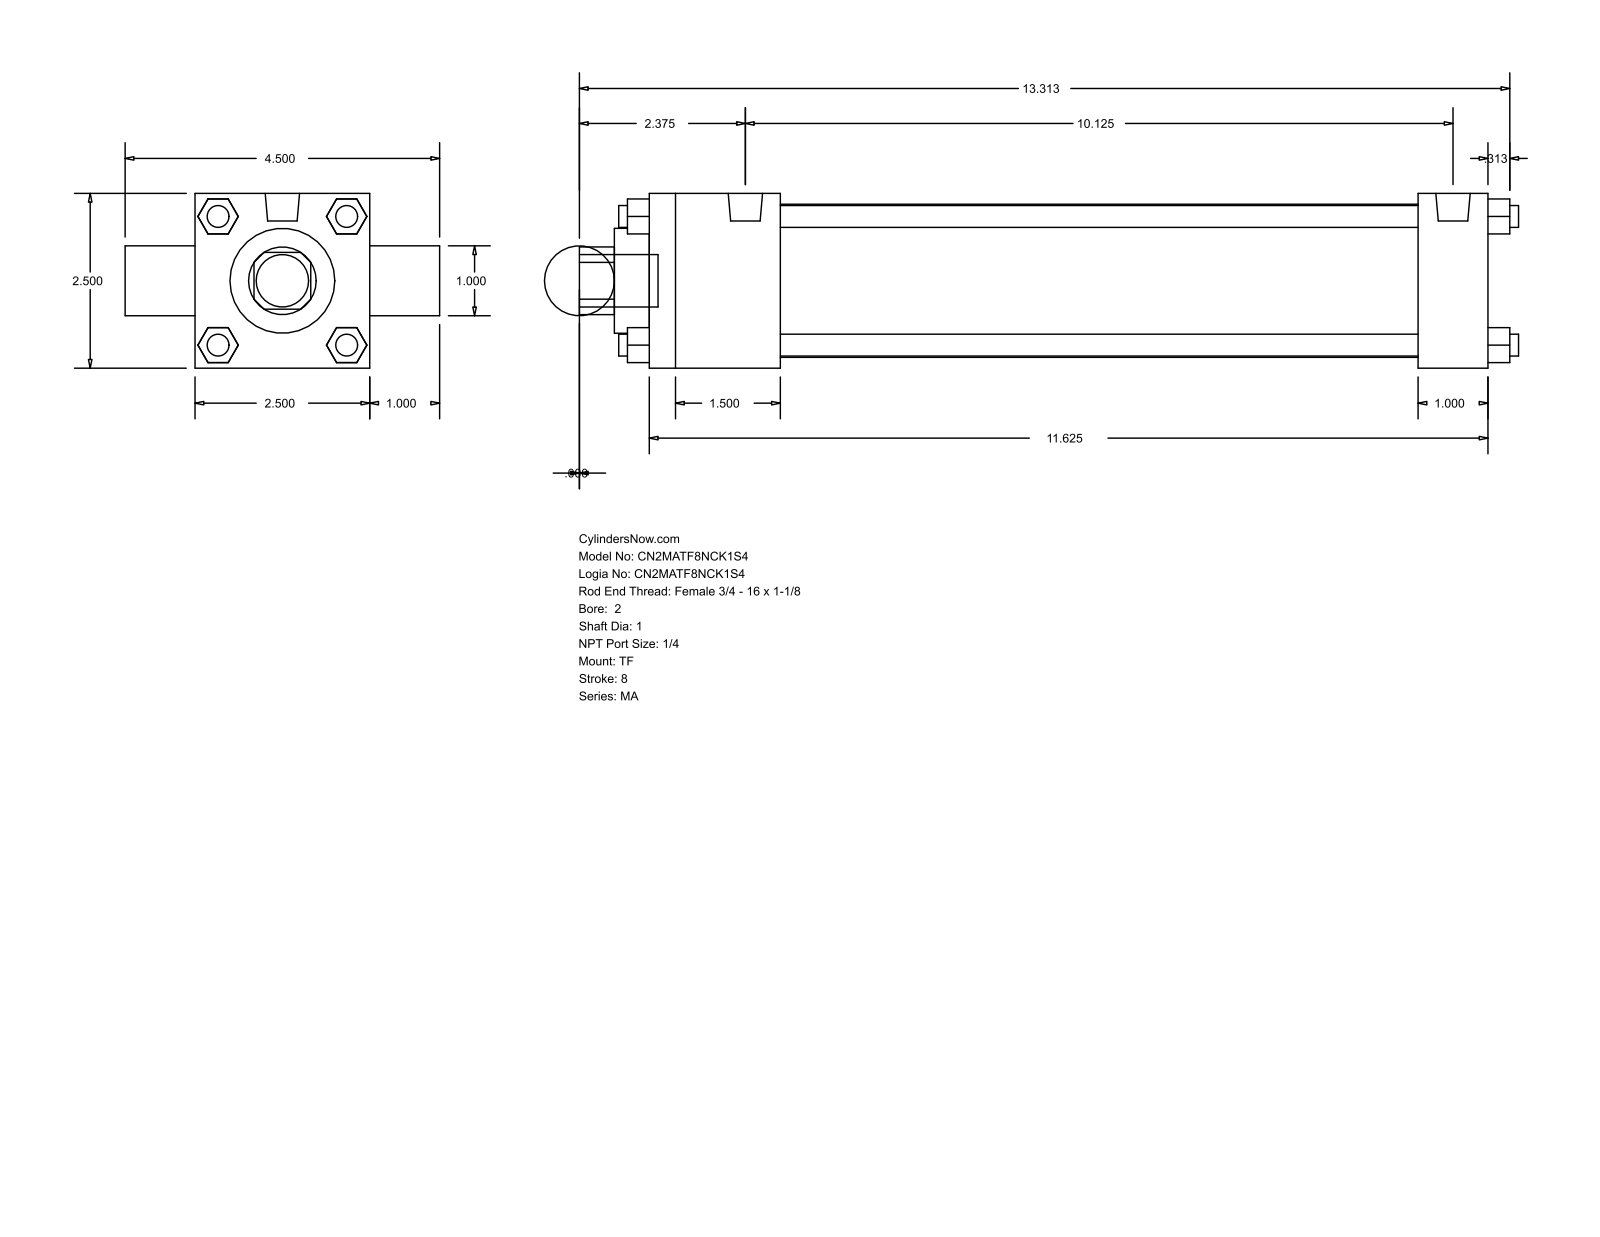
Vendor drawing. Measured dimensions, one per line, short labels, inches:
name: MA_TF__0200_1
written by: GSSL Pune (CONFIG_CONTROL_DESIGN)
unit: in
bodies: 0 solids, 120 faces (92 planar, 28 cylindrical, 0 other)
size: 13.437 × 4.5 × 2.5
holes: 2× ⌀1, 1× ⌀1.5, 1× ⌀2.19
bosses: 7× ⌀0.313, 2× ⌀0.492, 1× ⌀0.75
rounds: 1× R0.484
face distances: 2.5, 1, 12, 0.5, 1.875, 11, 9.125, 10.125, 3.5, 0.92
